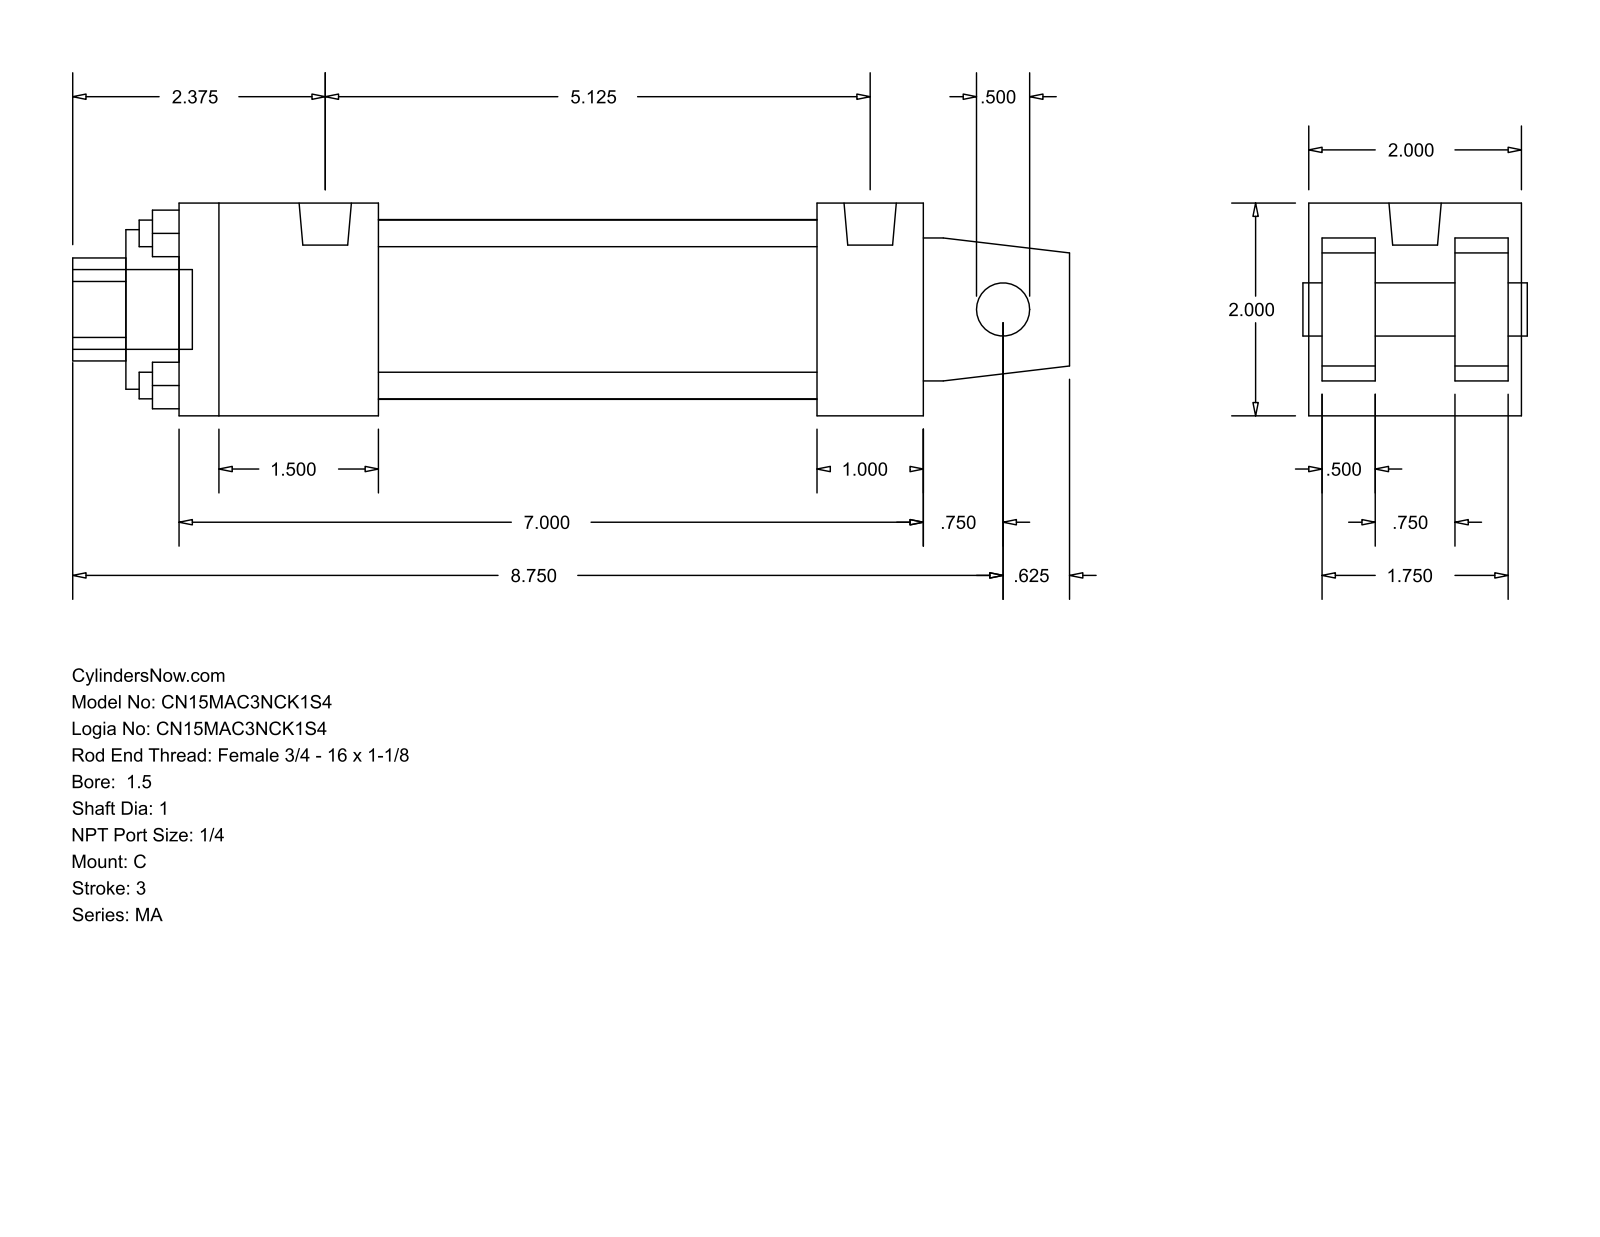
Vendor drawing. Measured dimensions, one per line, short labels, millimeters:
name: MA_C__0150_1
written by: GSSL Pune (CONFIG_CONTROL_DESIGN)
unit: mm
bodies: 0 solids, 103 faces (76 planar, 27 cylindrical, 0 other)
size: 238.12 × 50.8 × 50.8
holes: 4× ⌀6.35, 1× ⌀12.7, 1× ⌀25.4, 1× ⌀38.1, 1× ⌀42.93
bosses: 4× ⌀7.94, 2× ⌀12.49, 1× ⌀19.05
rounds: 1× R12.29
face distances: 50.8, 47.63, 12.7, 3.17, 15.87, 34.93, 31.76, 44.46, 177.8, 25.4
hole spacings: 25.68, 36.32, 51.36
